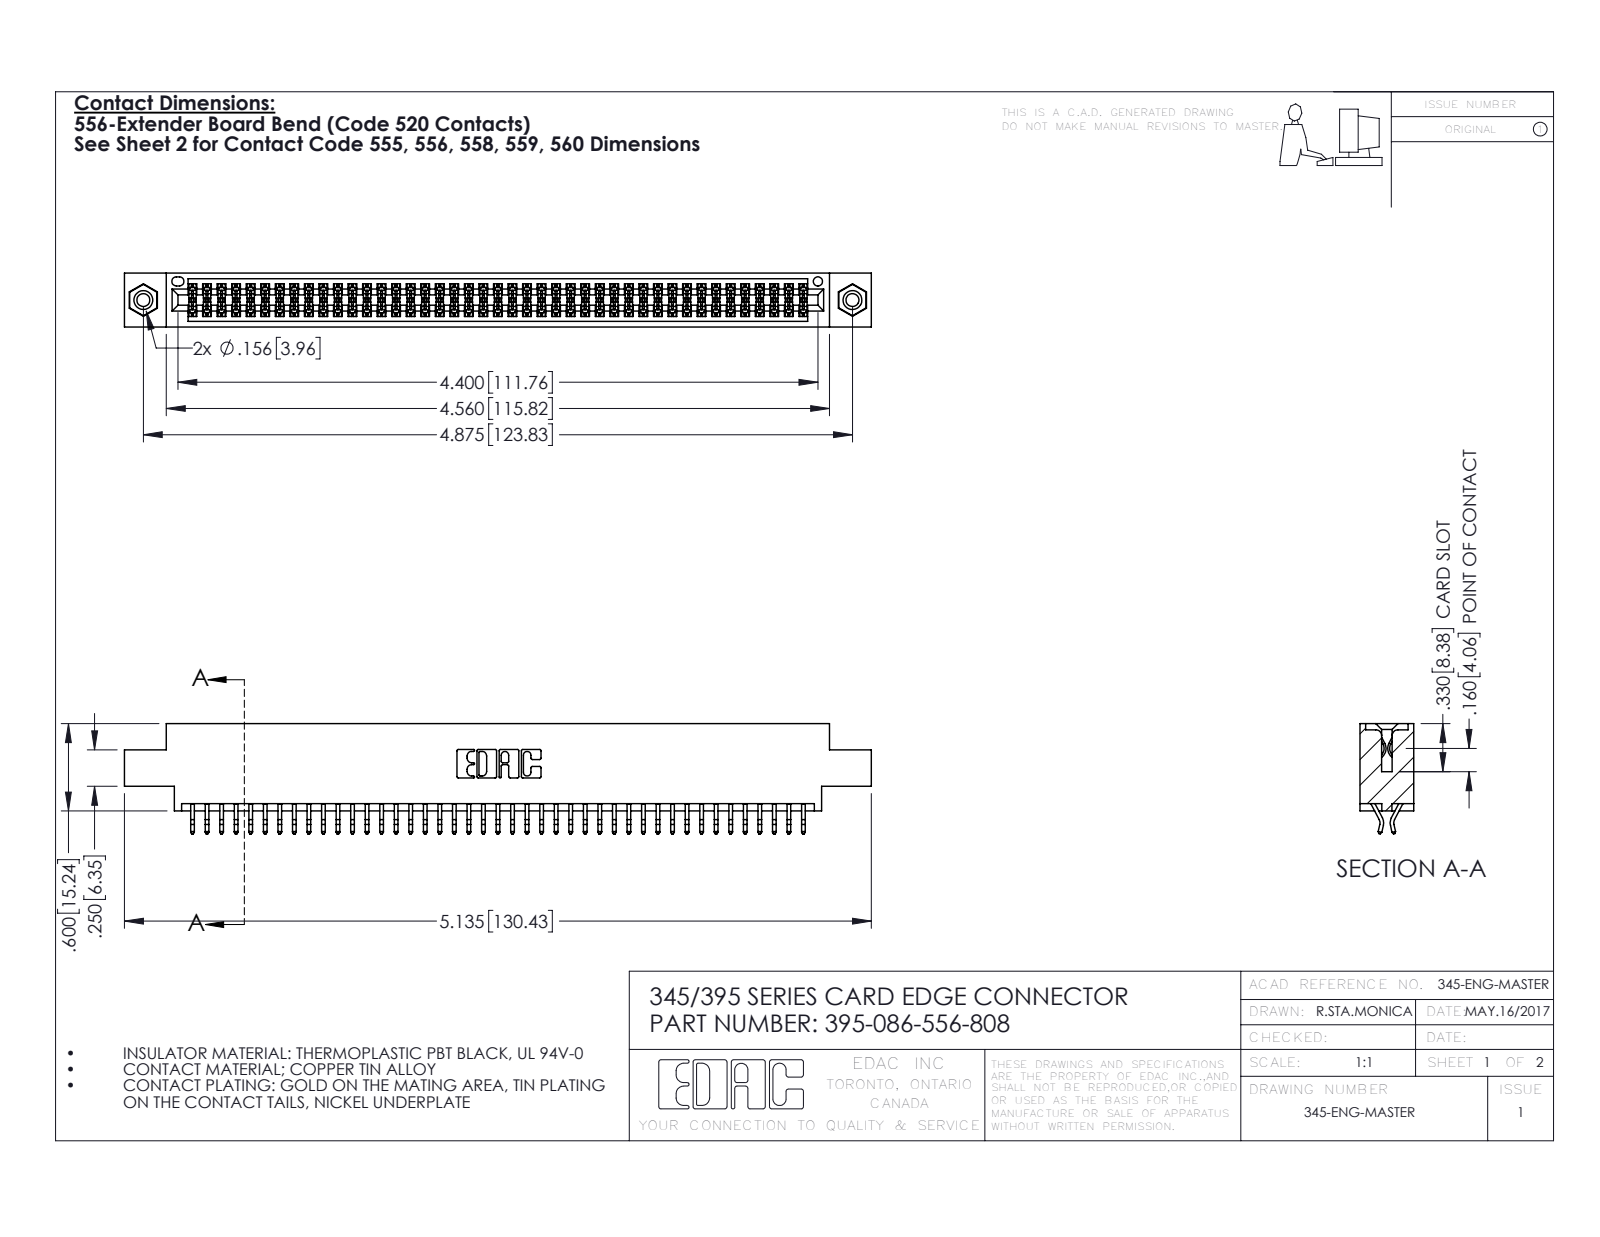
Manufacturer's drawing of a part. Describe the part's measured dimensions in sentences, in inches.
The part is named "395-086-556-808; 345 Part_0.170 Offset - 0.156 Dia-TI; 345-250-001_345-250-003-102; 345-292-001_556 Tail". Its 3-D file was written by "SolidWorks 2016 (CONFIG_CONTROL_DESIGN)". It is 89 solids with 5006 faces: 3298 planar, 1692 cylindrical and 16 other. Overall it measures 5.135 by 0.757 by 0.37 inches. Its volume is 0.766 cubic inches and its surface area 28.92 square inches. Round holes: 2 of diameter 0.089, 2 of diameter 0.125, 2 of diameter 0.156, 1 of diameter 0.064. Round bosses or shafts: 2 of diameter 0.155. Partial cylindrical surfaces (rounded edges, fillets, slot ends): 129 of radius 0.006, 22 of radius 0.01, 6 of radius 0.007, 6 of radius 0.031, 3 of radius 0.026, 2 of radius 0.01, 2 of radius 0.014, 2 of radius 0.019. The main face-to-face distances are 0.072, 0.298, 0.37, 0.2, 0.025, 0.098, 0.272, 0.225, 0.175, 0.149. The hole center spacings are 0.27, 4.639, 4.875.
